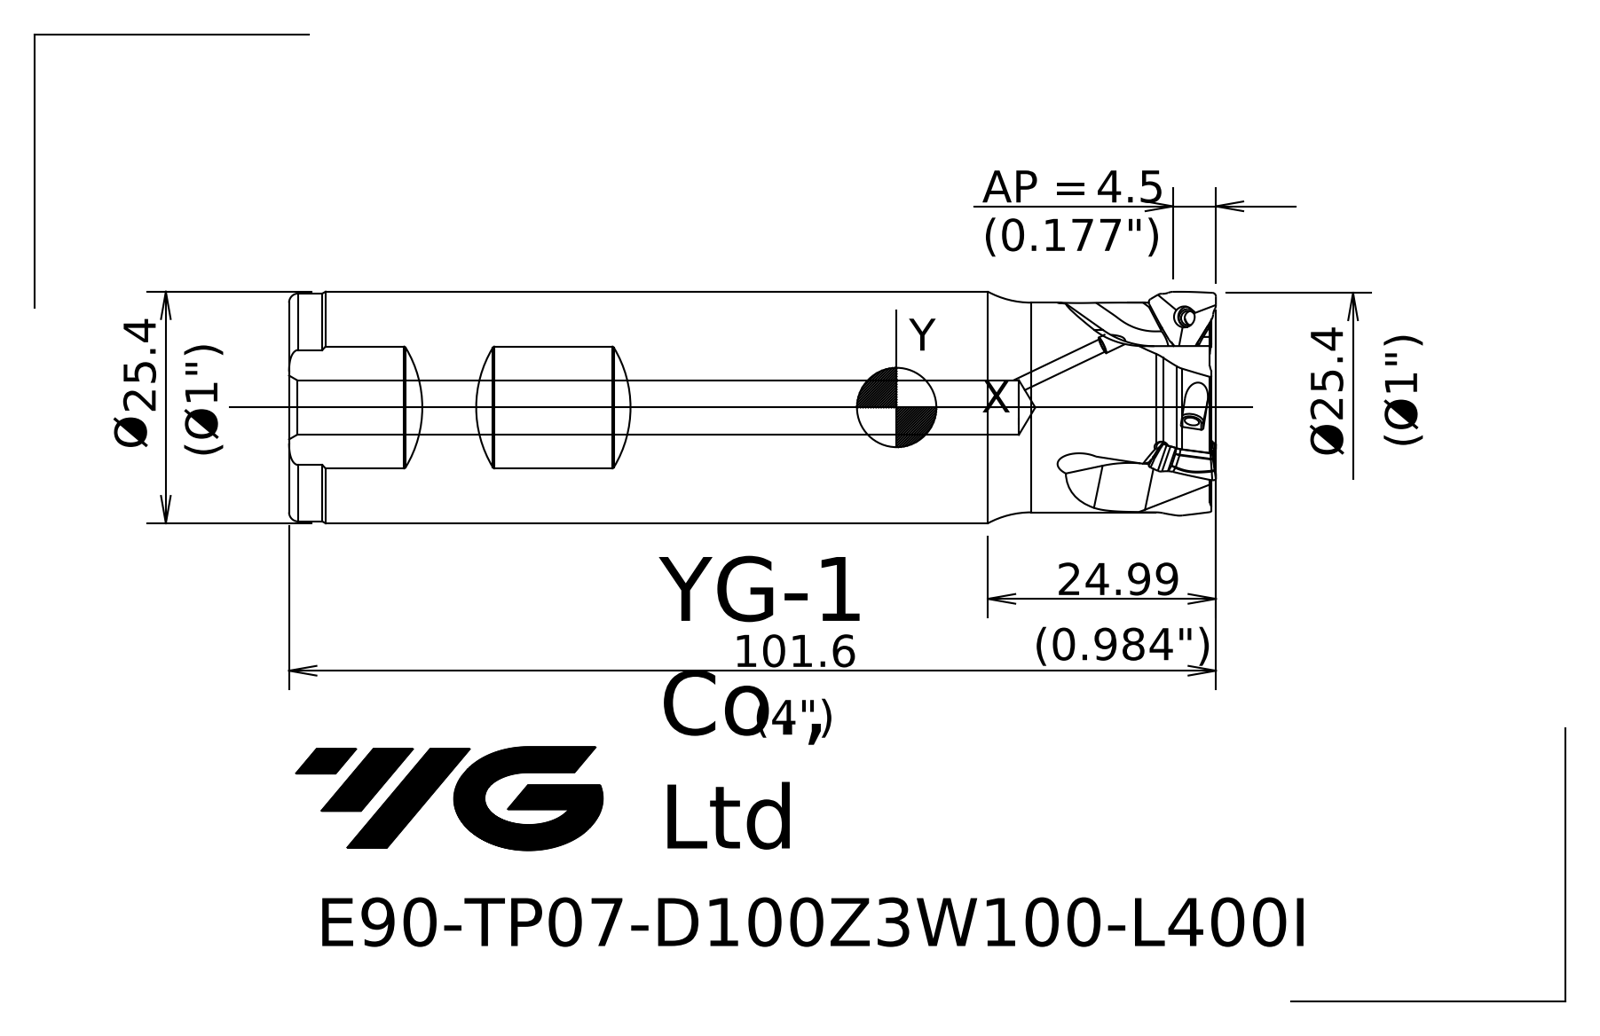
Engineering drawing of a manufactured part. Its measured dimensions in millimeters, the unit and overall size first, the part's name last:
Units: millimetres
Overall size (bounding box): 101.6 × 25.45 × 25.45
Round holes (diameter × count): ⌀1.5 ×1, ⌀6 ×1
Round bosses / shafts (diameter × count): ⌀25.4 ×1, ⌀25 ×1, ⌀23 ×1
Partial cylindrical surfaces — rounded edges, fillets, slot ends (radius × count): R0.3 ×3
Main face-to-face distances: 100.95, 101.1, 16.13
Volume: 46 401 mm³ · Surface area: 11 760 mm²
Bodies: 1 solid, 51 faces (8 planar, 8 cylindrical, 35 other)
Part name (STEP PRODUCT): 10223E688571ypob
STEP written by: SIEMENS PLM Software NX 10.0 (AP203_CONFIGURATION_CONTROLLED_3D_DESIGN_OF_MECHANICAL_PARTS_AND_ASSEMBLIES_MIM_LF)
